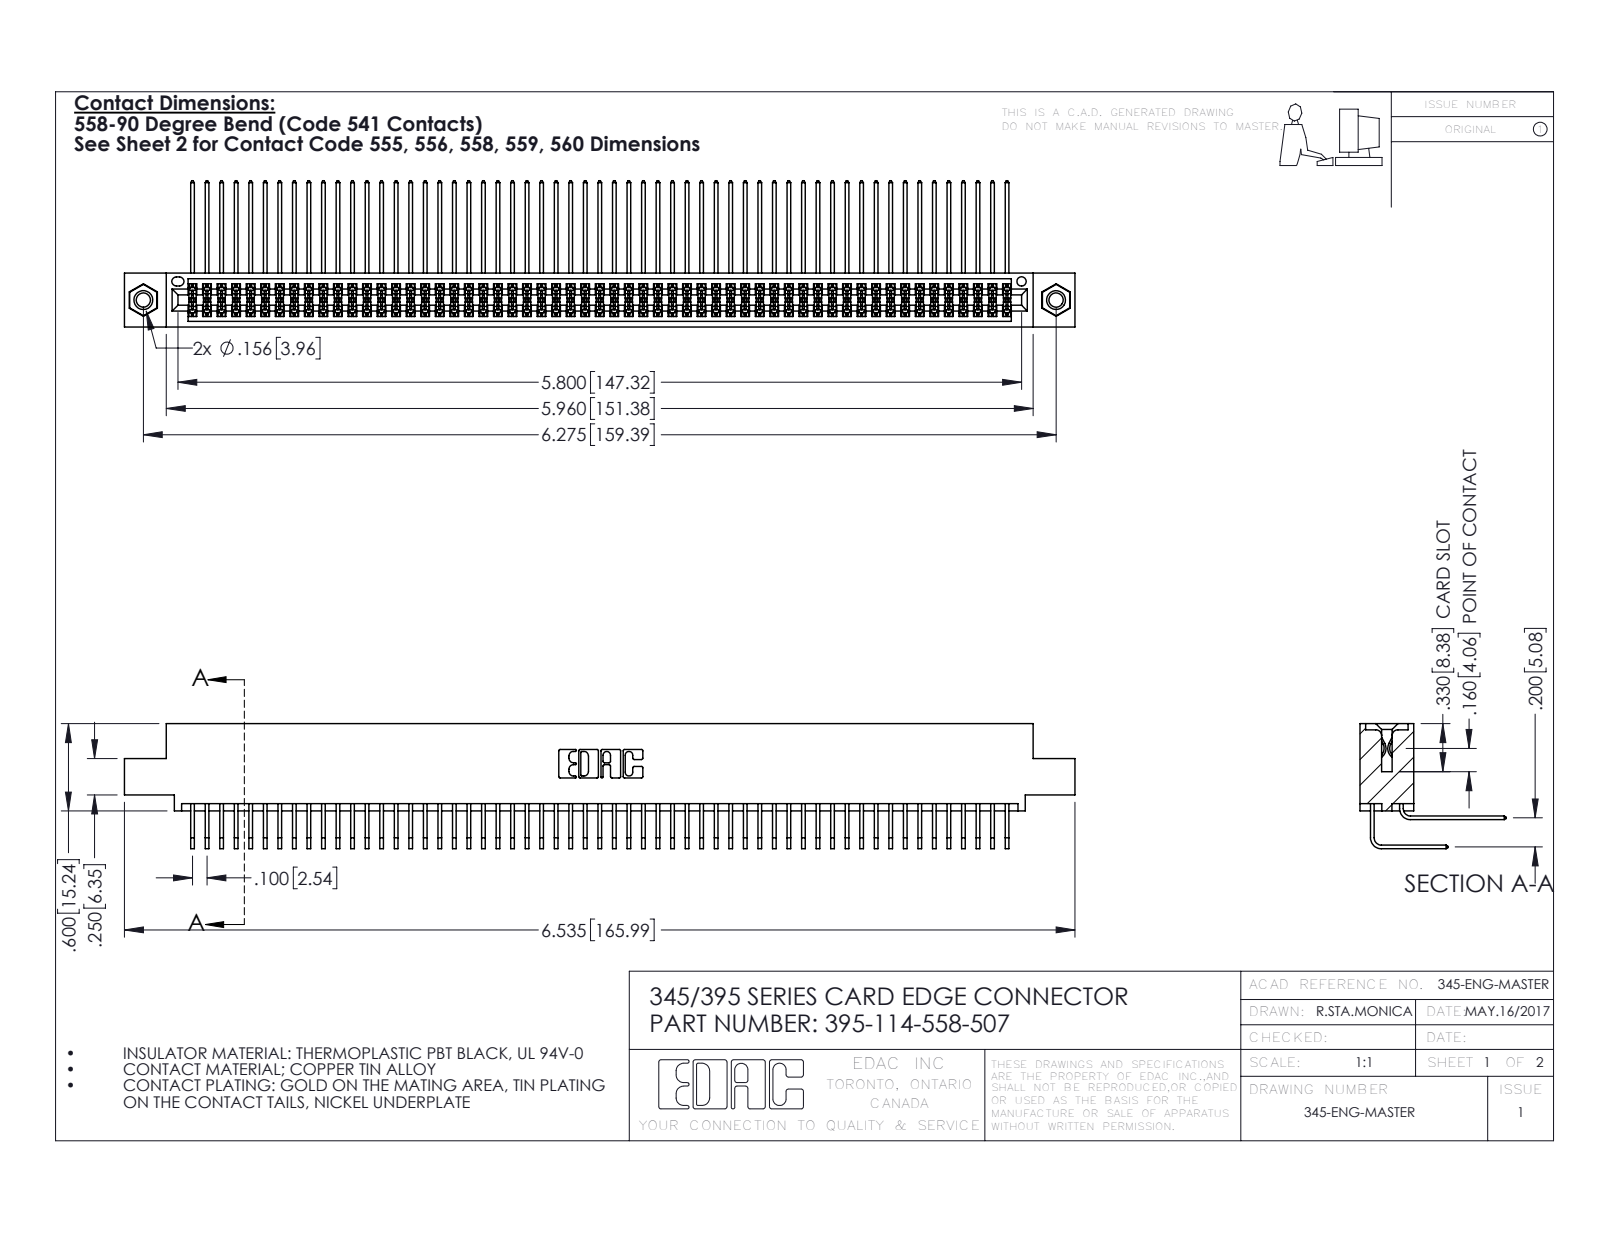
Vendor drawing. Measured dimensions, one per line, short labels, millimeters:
name: 395-114-558-507; 345-250-001_345-250-005-103; 345-292-001_558 Tail - 2; 345 Part_0.110 Offset - 0.156 Dia-TI (+1 more)
written by: SolidWorks 2016 (CONFIG_CONTROL_DESIGN)
unit: mm
bodies: 117 solids, 6118 faces (4106 planar, 1996 cylindrical, 16 other)
size: 166 × 25.5 × 21.8
volume: 16 830 mm³; area: 28 390 mm²
holes: 2× ⌀2.5, 2× ⌀3.2, 2× ⌀4, 1× ⌀1.6
bosses: 2× ⌀3.9
rounds: 172× R0.2, 22× R0.3, 6× R0.2, 6× R0.8, 3× R0.7, 2× R0.4, 2× R0.5, 2× R0.6
face distances: 1.8, 7.6, 5.1, 9.4, 2.5, 6.9, 0.6, 5.7, 0.6, 4.4
hole spacings: 6.9, 153.4, 159.4
